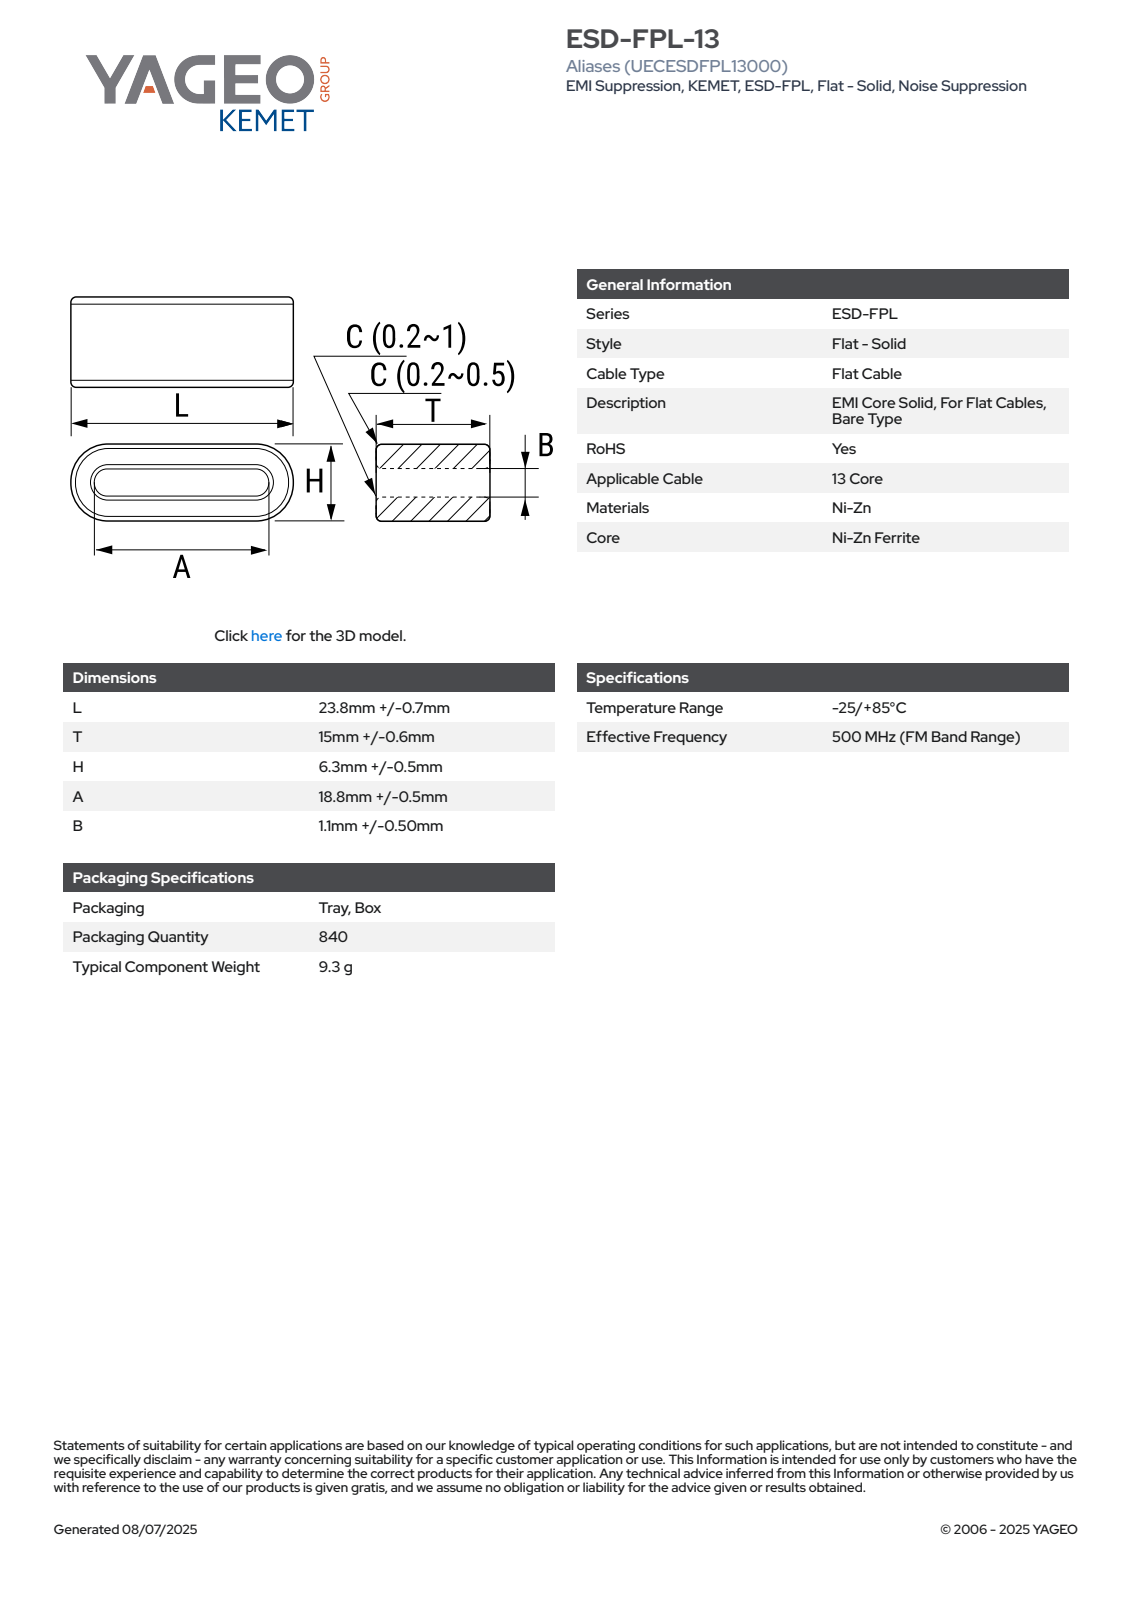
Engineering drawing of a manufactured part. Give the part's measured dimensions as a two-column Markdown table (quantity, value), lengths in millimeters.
| quantity | value |
| --- | --- |
| part name | EC_FPL3_L24.5T15.6H6.8A18.8B1.1 |
| STEP written by | SolidWorks 2021 (AUTOMOTIVE_DESIGN) |
| units | millimeters |
| bodies | 4 solids, 95 faces (63 planar, 16 cylindrical, 16 other) |
| overall size | 24.5 × 15.6 × 6.8 |
| volume | 2 124 mm³ |
| surface area | 1 772 mm² |
| partial cylindrical surfaces (radius × count) | 0.2 × 8, 0.55 × 2, 3.4 × 2 |
| main face-to-face distances | 2.85, 3.95, 6.8, 1.1, 15.6, 6.79, 8.81, 2.02, 7.18, 8.42 |
